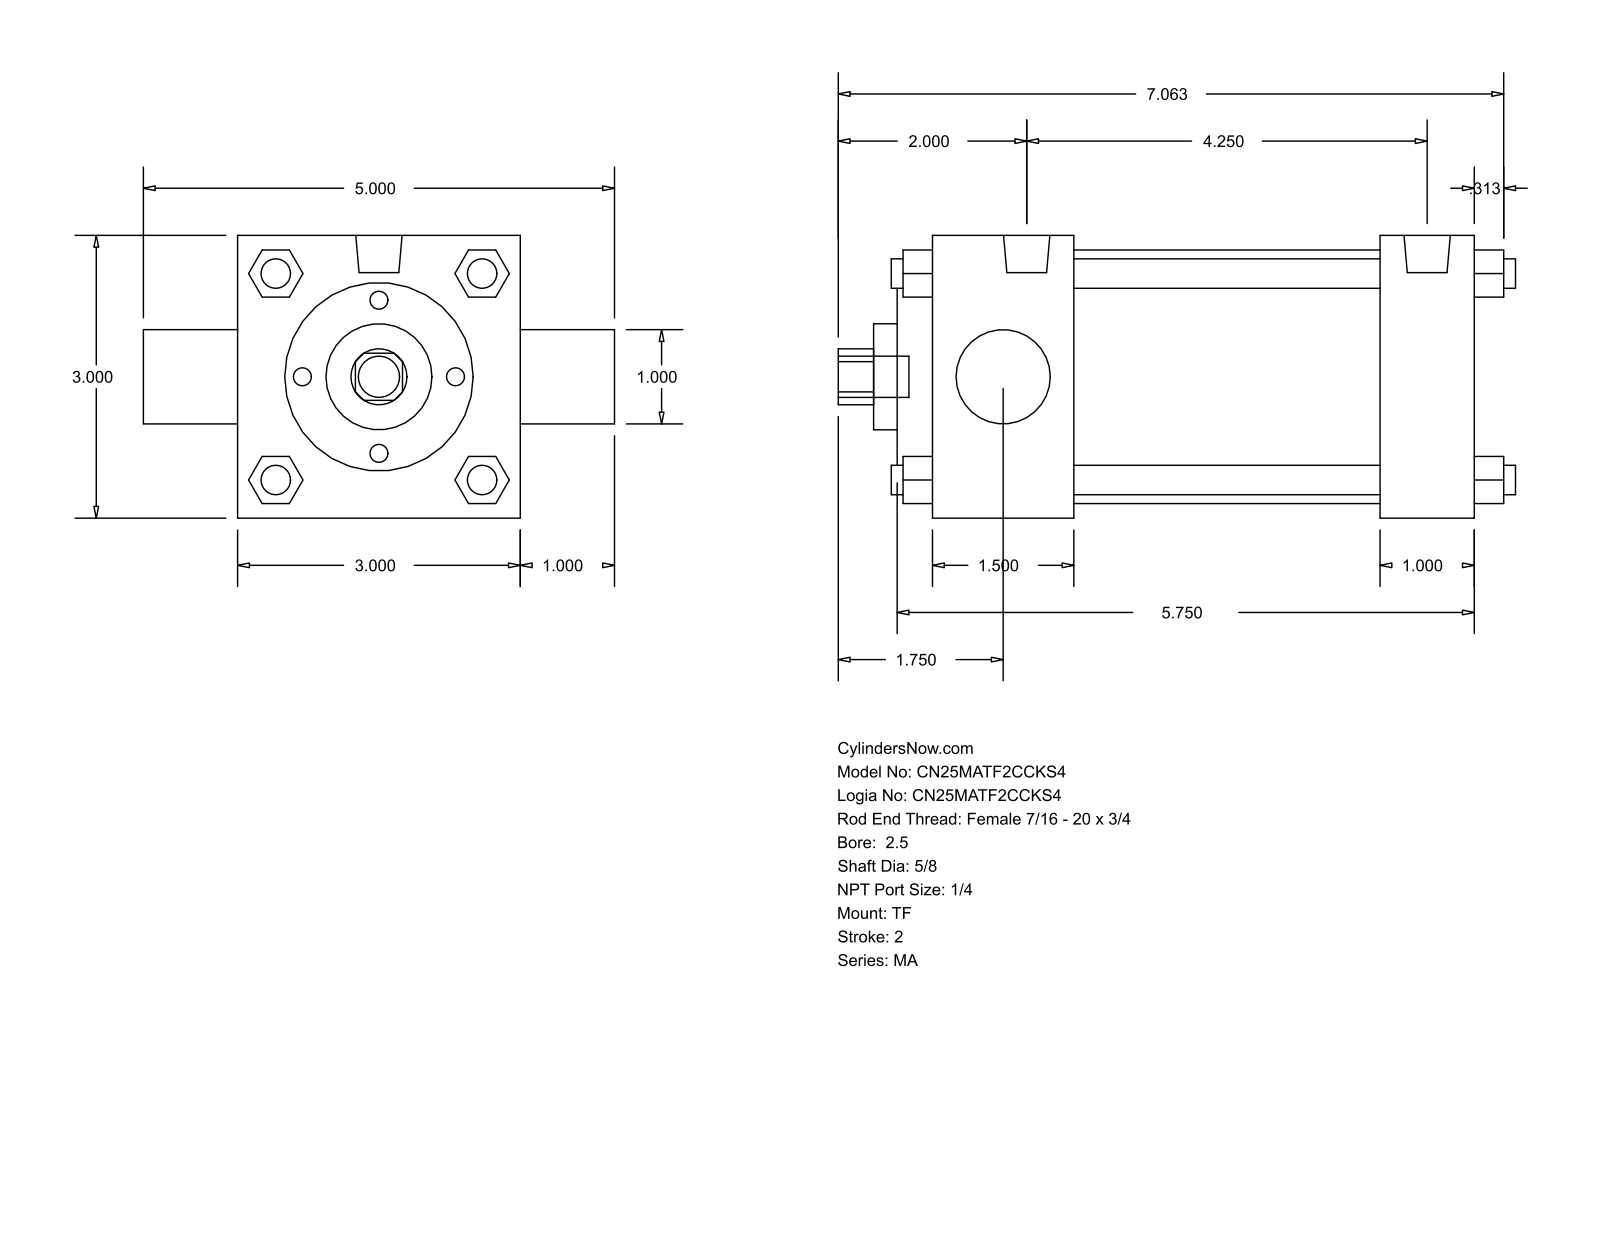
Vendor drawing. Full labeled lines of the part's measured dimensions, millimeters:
Part name (STEP PRODUCT): MA_TF__0250_0.625
STEP written by: GSSL Pune (CONFIG_CONTROL_DESIGN)
Units: millimetres
Bodies: 0 solids, 122 faces (93 planar, 29 cylindrical, 0 other)
Overall size (bounding box): 182.56 × 127 × 76.2
Round holes (diameter × count): ⌀15.88 ×1, ⌀25.4 ×1, ⌀28.57 ×1, ⌀50.8 ×1, ⌀68.33 ×1
Round bosses / shafts (diameter × count): ⌀7.94 ×7, ⌀12.49 ×2, ⌀11.11 ×1
Partial cylindrical surfaces — rounded edges, fillets, slot ends (radius × count): R7.54 ×1
Main face-to-face distances: 76.2, 146.05, 25.4, 38.1, 120.65, 82.55, 107.95, 12.7, 9.52, 47.62
